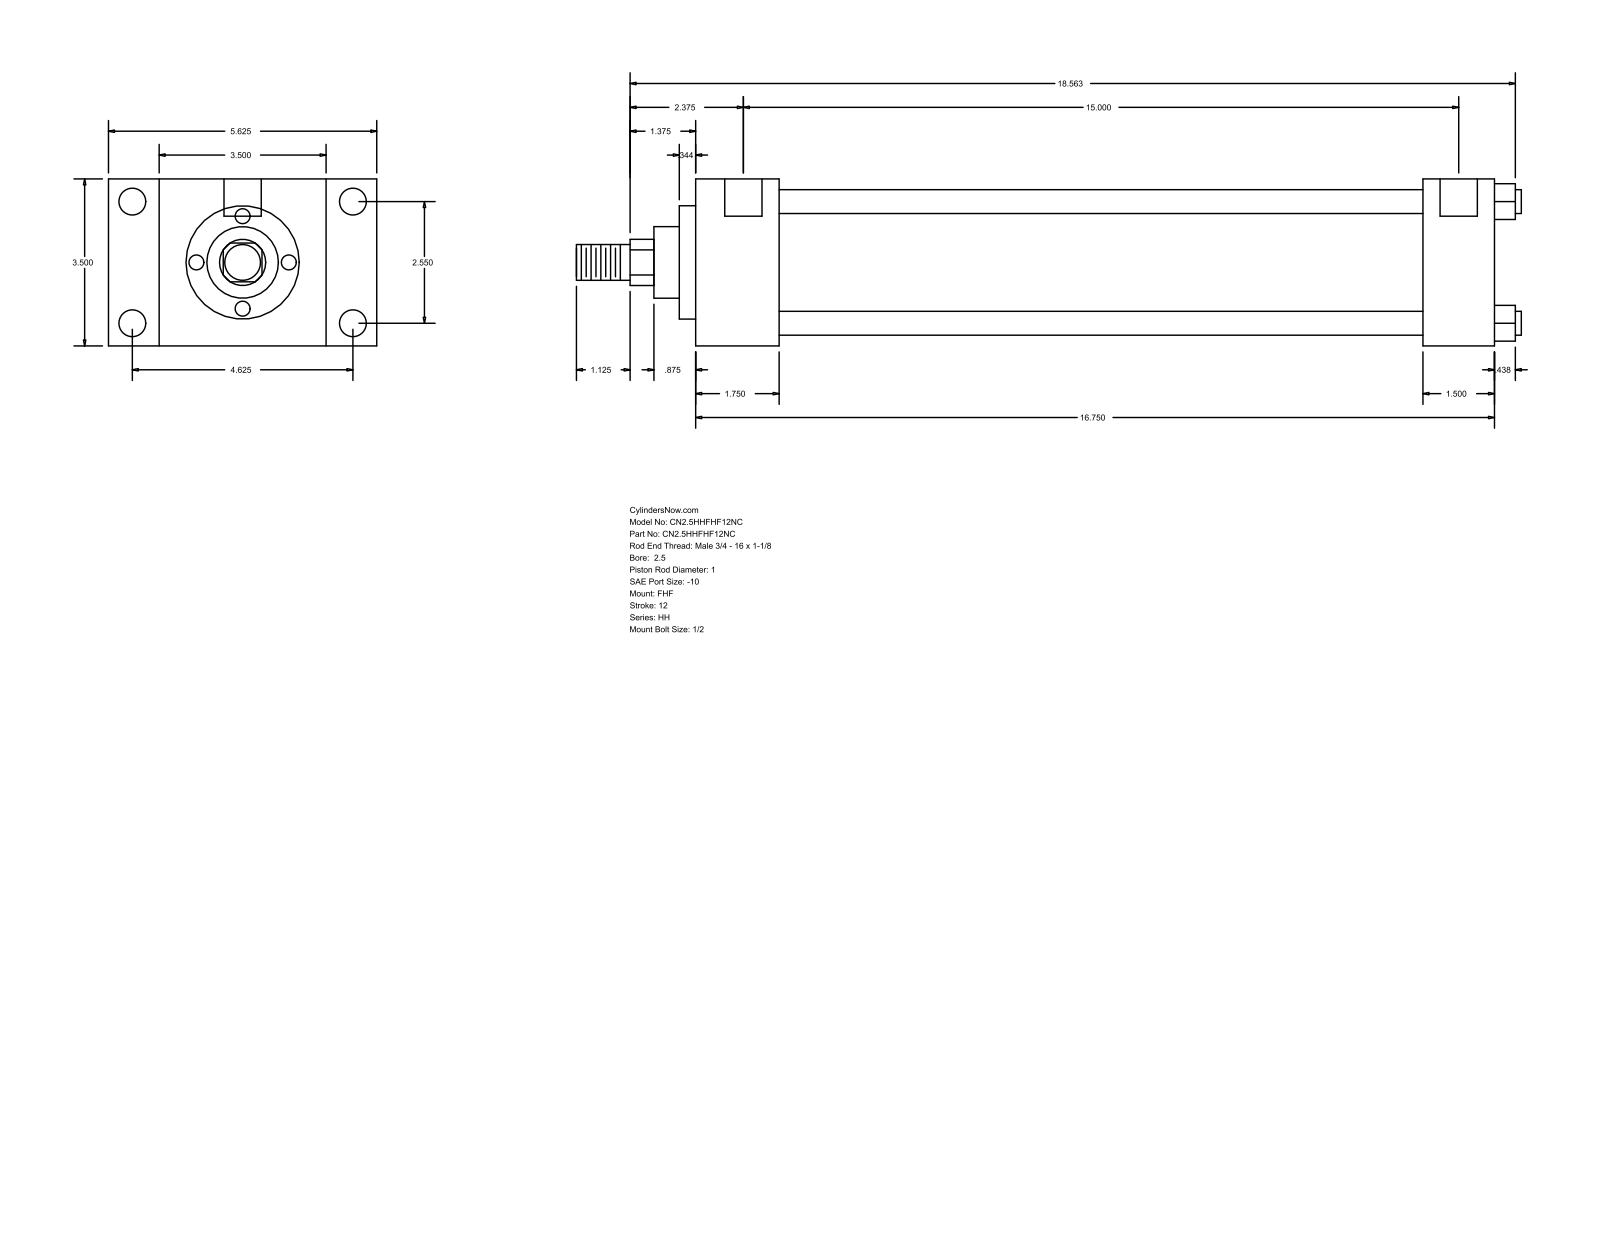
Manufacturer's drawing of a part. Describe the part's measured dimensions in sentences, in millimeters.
The part is named "HH_FHF__0250_1". Its 3-D file was written by "GSSL Pune (CONFIG_CONTROL_DESIGN)". It is 0 solids with 90 faces: 61 planar, 29 cylindrical and 0 other. Overall it measures 503.24 by 142.88 by 88.9 millimeters. Round holes: 4 of diameter 5.56, 4 of diameter 14.3, 2 of diameter 19.84. Round bosses or shafts: 4 of diameter 12.7, 1 of diameter 73.03, 1 of diameter 60.33, 1 of diameter 38.1, 1 of diameter 25.4, 1 of diameter 19.05. Partial cylindrical surfaces (rounded edges, fillets, slot ends): 1 of radius 12.29. The main face-to-face distances are 88.9, 44.46, 26.99, 115.89, 425.46, 381, 142.88, 387.35, 342.89, 38.11. The hole center spacings are 1.59, 64.76, 117.48, 134.15, 382.58, 384.17, 380.99.
